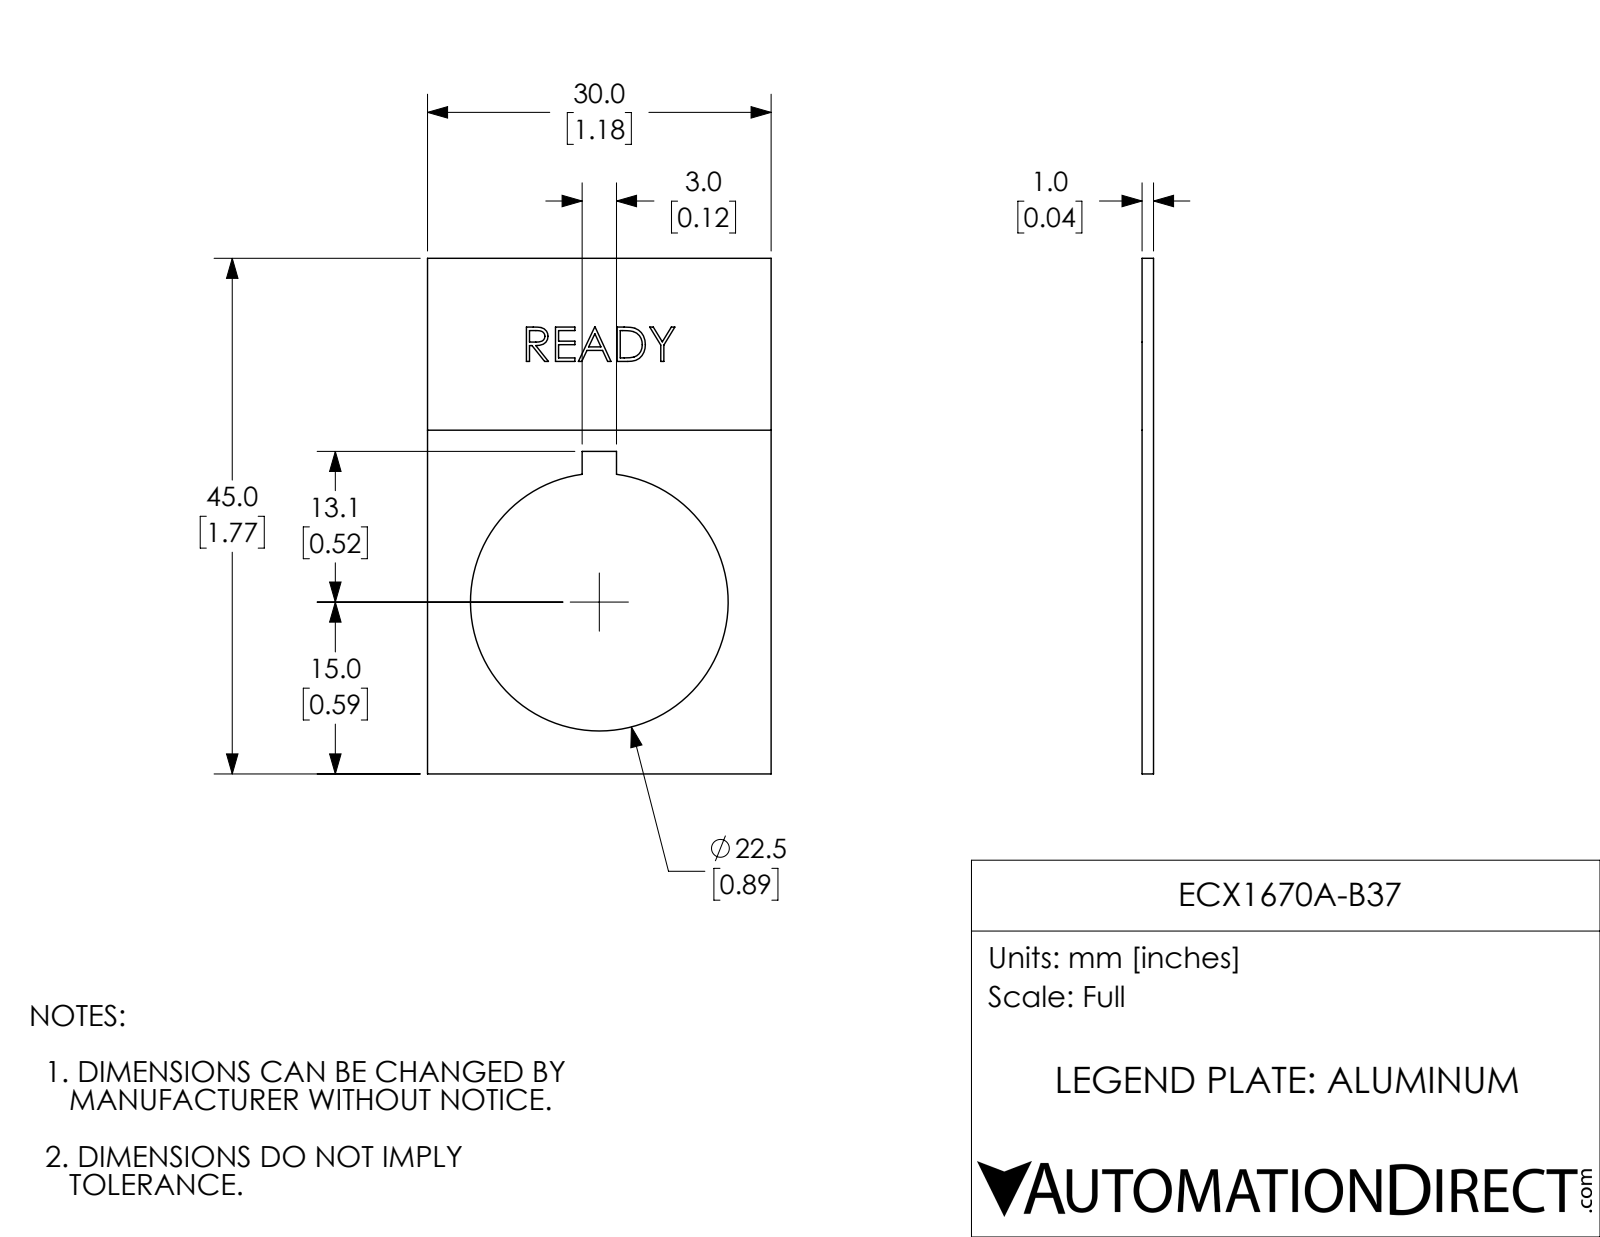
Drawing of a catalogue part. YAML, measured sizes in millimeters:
part_name: "ECX1670A-B37"
step_written_by: "SolidWorks 2017 (AUTOMOTIVE_DESIGN)"
units: millimeters
bodies: {solids: 1, faces: 82, planar: 67, cylindrical: 3, other: 12}
overall_size: [45, 30, 1]
volume: 950
surface_area: 2120
round_holes:
  - {diameter: 22.5, count: 1}
face_to_face_distances: [1, 30, 45, 1, 13.5, 16.5, 28.1, 16.8, 3, 0.3]
